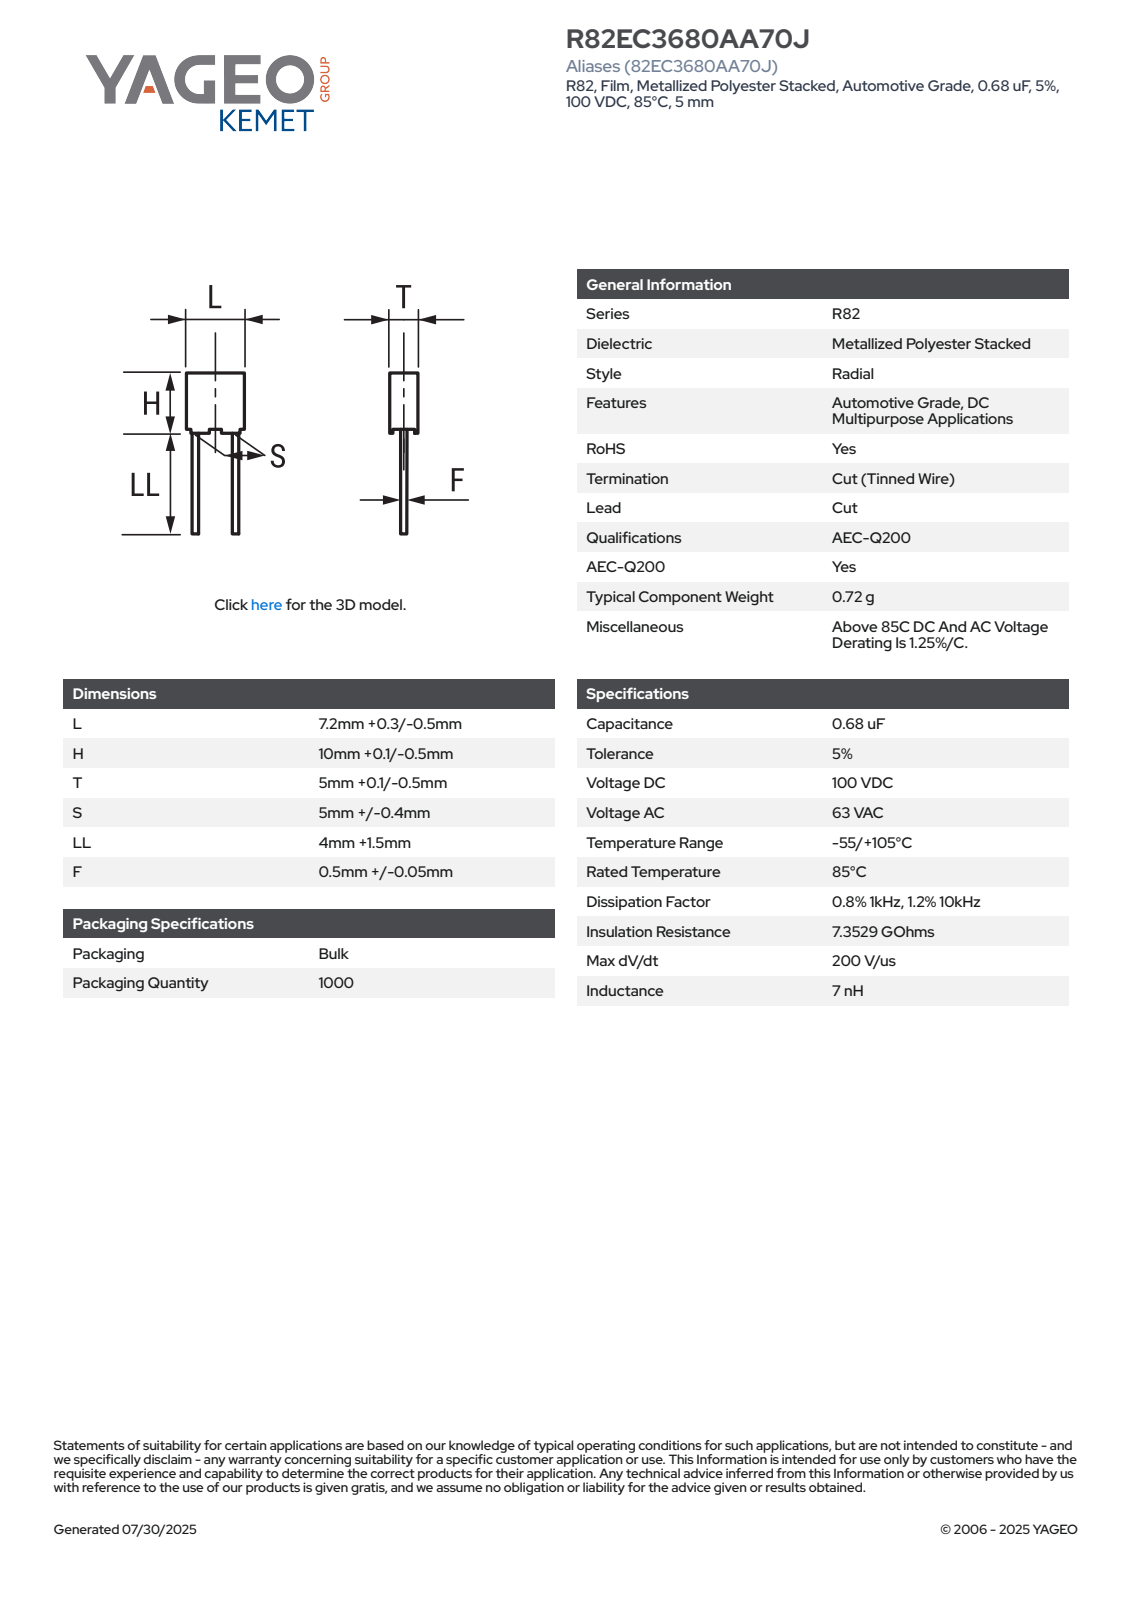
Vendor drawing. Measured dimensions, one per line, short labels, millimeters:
name: CFR_RB3_7.2X10X5_L7.5H10.1T5.1S5LL5.5F0.55
written by: SolidWorks 2014 (AUTOMOTIVE_DESIGN)
unit: mm
bodies: 4 solids, 85 faces (77 planar, 8 cylindrical, 0 other)
size: 15.6 × 7.5 × 5.11
volume: 364 mm³; area: 366 mm²
bosses: 2× ⌀0.55
rounds: 4× R0.5
face distances: 5.1, 7.5, 9.35, 4.85, 7.25, 0.75, 10.1, 4.6, 7, 0.35
